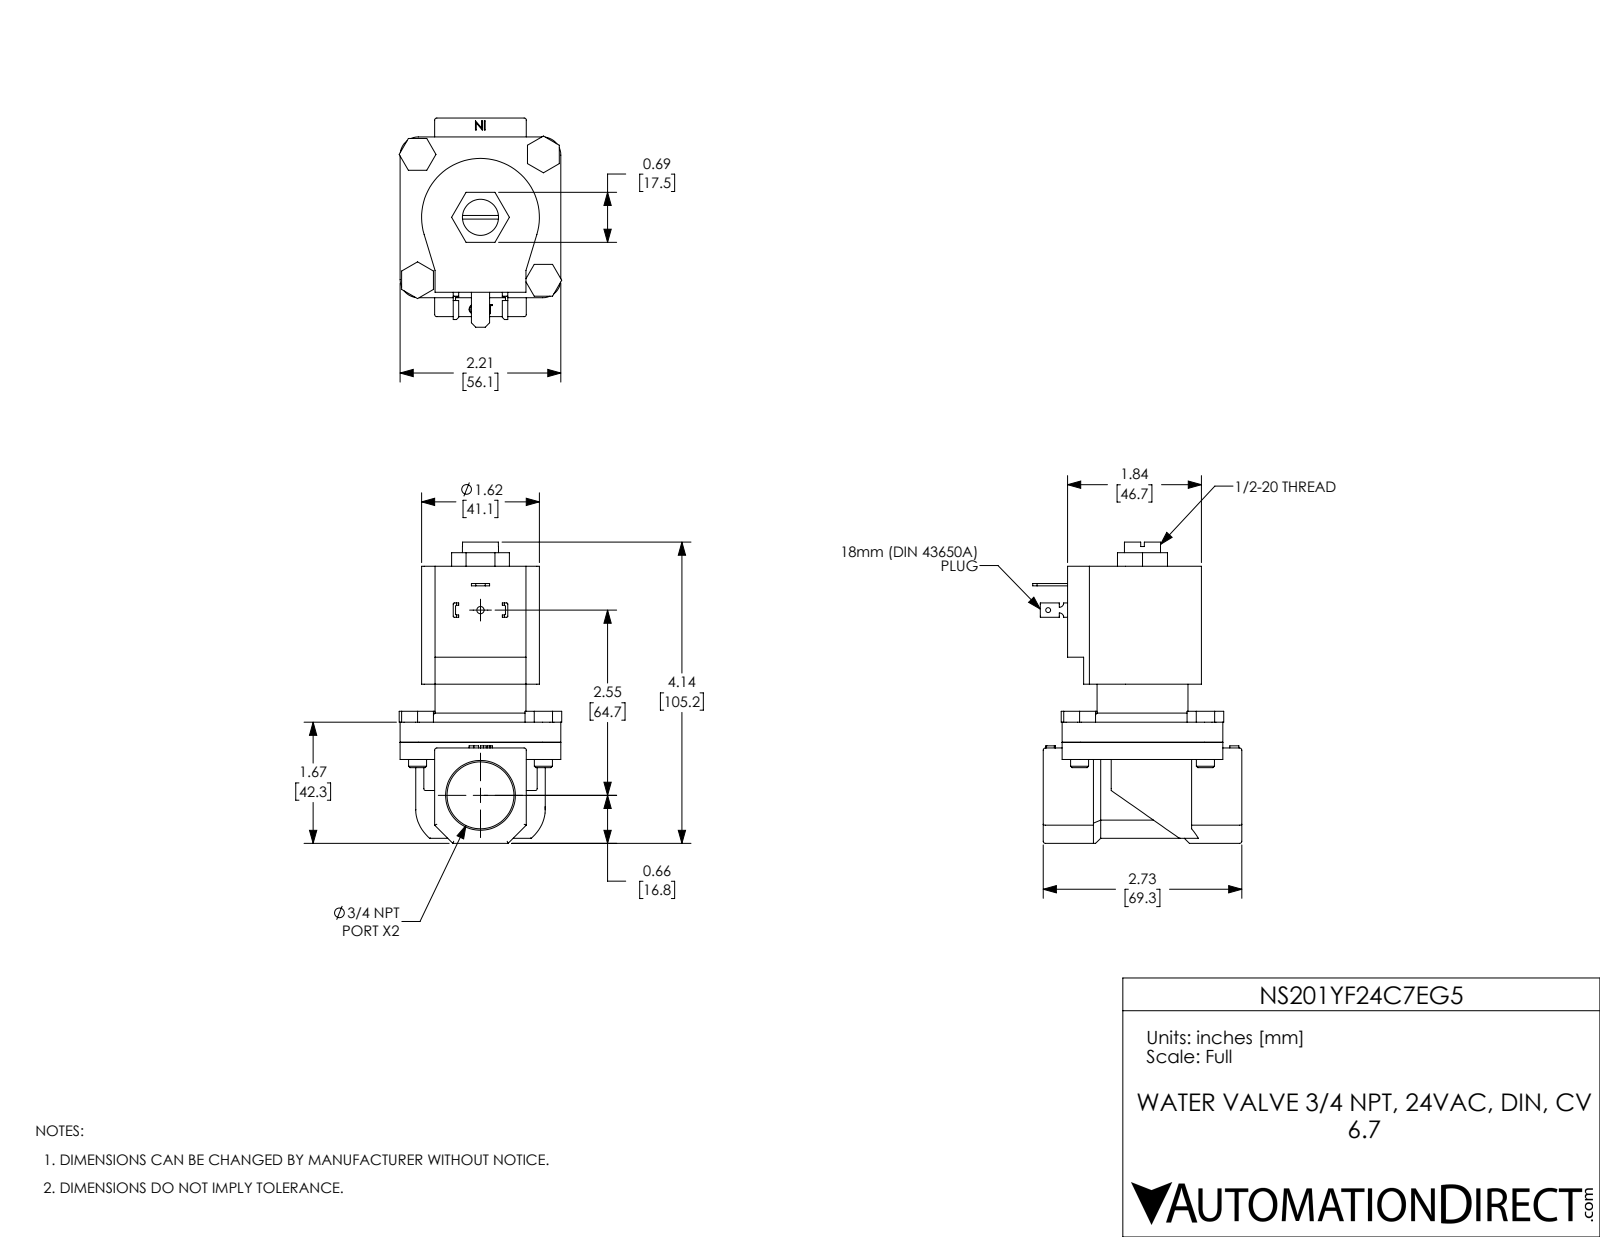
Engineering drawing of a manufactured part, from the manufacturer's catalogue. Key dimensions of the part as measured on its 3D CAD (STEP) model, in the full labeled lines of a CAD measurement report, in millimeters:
Part name (STEP PRODUCT): NS201YF24C7EG5
STEP written by: SolidWorks 2021 (CONFIG_CONTROL_DESIGN)
Units: millimetres
Bodies: 11 solids, 332 faces (198 planar, 99 cylindrical, 35 other)
Overall size (bounding box): 105.2 × 73 × 56.8
Volume: 169 100 mm³ · Surface area: 43 300 mm²
Round holes (diameter × count): ⌀6.4 ×4, ⌀1.7 ×1, ⌀2.5 ×1, ⌀12.6 ×1, ⌀13 ×1, ⌀23.4 ×1, ⌀29.3 ×1
Round bosses / shafts (diameter × count): ⌀6.3 ×4, ⌀31.8 ×1
Partial cylindrical surfaces — rounded edges, fillets, slot ends (radius × count): R0.8 ×15, R0.4 ×8, R6.4 ×4, R1.5 ×2, R20.6 ×1, R22.6 ×1
Main face-to-face distances: 7, 61.4, 54.4, 12.1, 44.1, 56.1, 6, 13, 67.4, 6.6
Hole centre spacings: 31.1, 43.9, 62.1, 64.7
